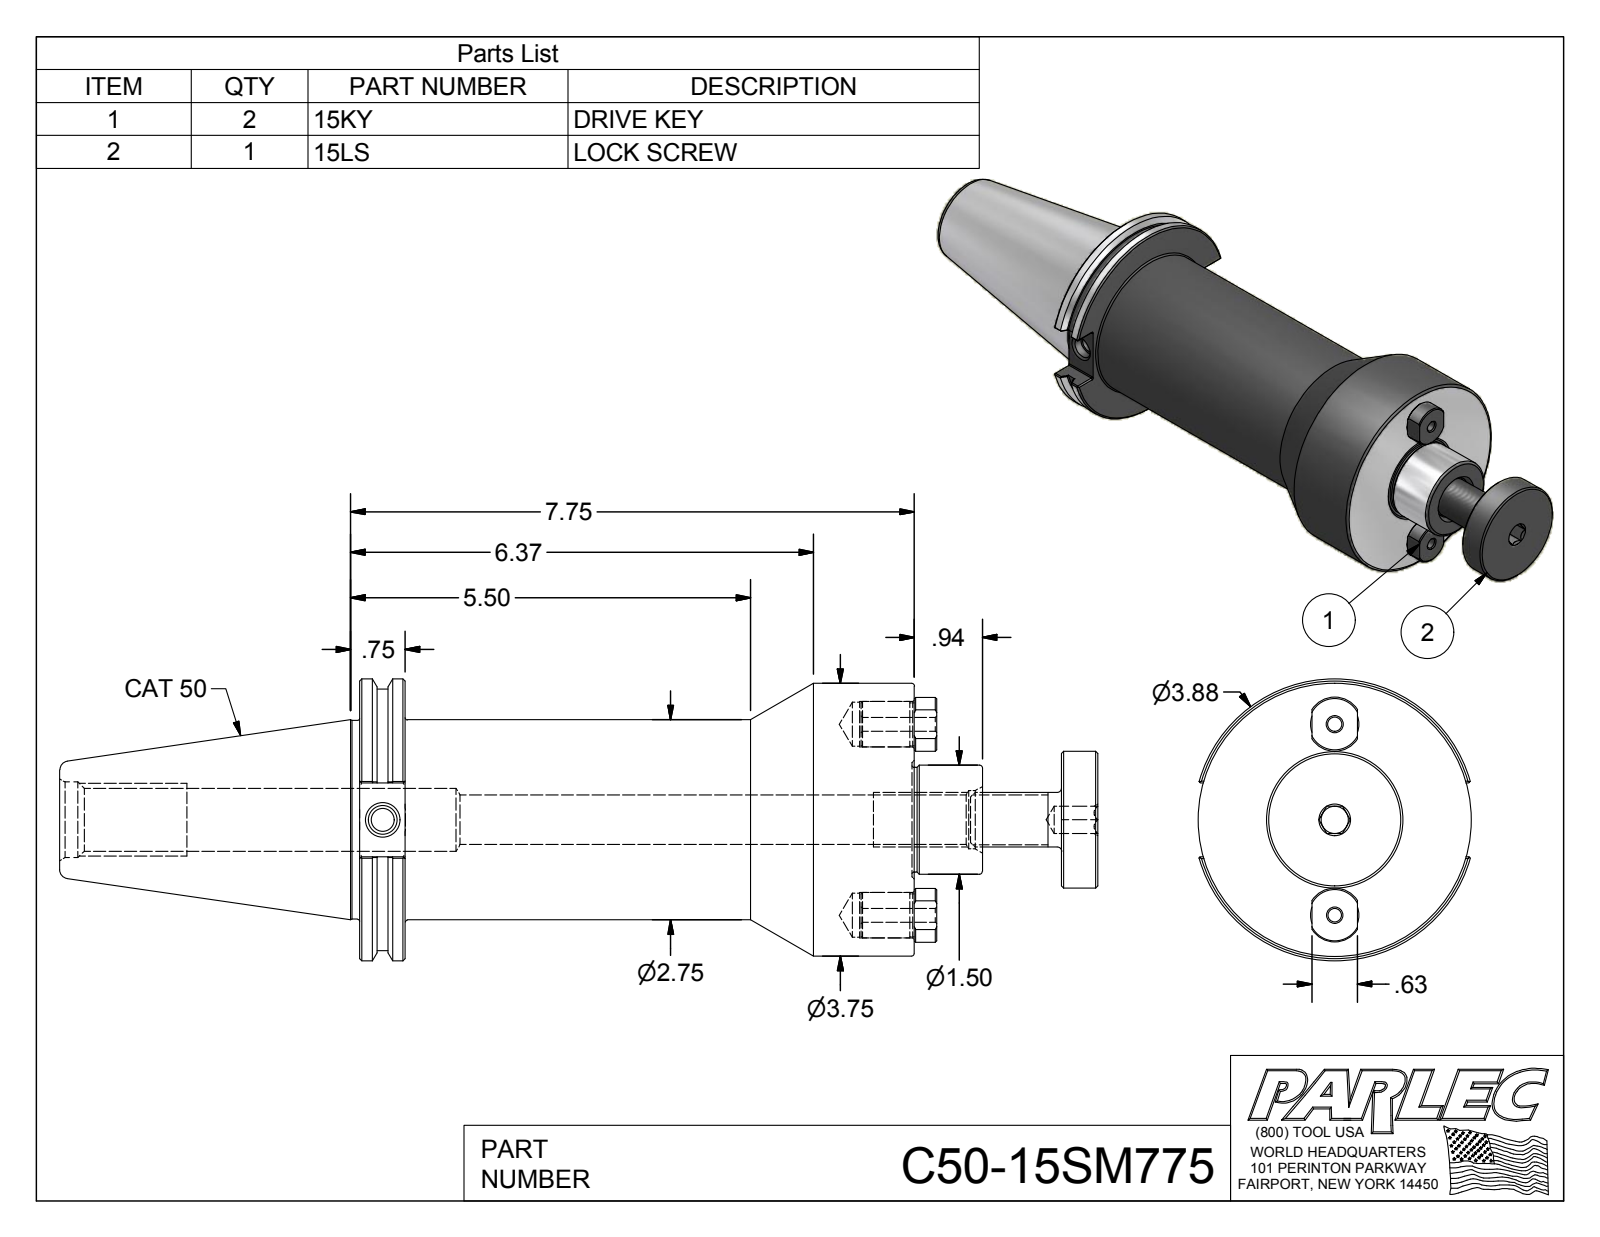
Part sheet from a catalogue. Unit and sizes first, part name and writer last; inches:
Units: inches
Overall size (bounding box): 14.275 × 3.875 × 3.75
Round holes (diameter × count): ⌀0.19 ×2, ⌀0.604 ×2, ⌀0.624 ×2, ⌀0.315 ×1, ⌀0.375 ×1, ⌀0.399 ×1, ⌀0.682 ×1, ⌀0.8 ×1, ⌀0.865 ×1, ⌀1.038 ×1
Round bosses / shafts (diameter × count): ⌀0.626 ×2, ⌀0.59 ×2, ⌀3.875 ×1, ⌀3.75 ×1, ⌀3.594 ×1, ⌀2.75 ×1, ⌀2.73 ×1, ⌀1.88 ×1
Partial cylindrical surfaces — rounded edges, fillets, slot ends (radius × count): R0.02 ×12, R0.37 ×2
Main face-to-face distances: 0.625, 7.625, 7, 10.15, 9.525, 2.525, 9.65, 9.025, 2.025, 0.5
Hole centre spacings: 1.312, 1.312, 2.624
Volume: 70.58 in³ · Surface area: 185 in²
Bodies: 4 solids, 166 faces (62 planar, 46 cylindrical, 58 other)
Part name (STEP PRODUCT): C50-15SM775; C50-15SM775-1; 15LS; 15KY
STEP written by: Autodesk Inventor 2012 (AUTOMOTIVE_DESIGN)
